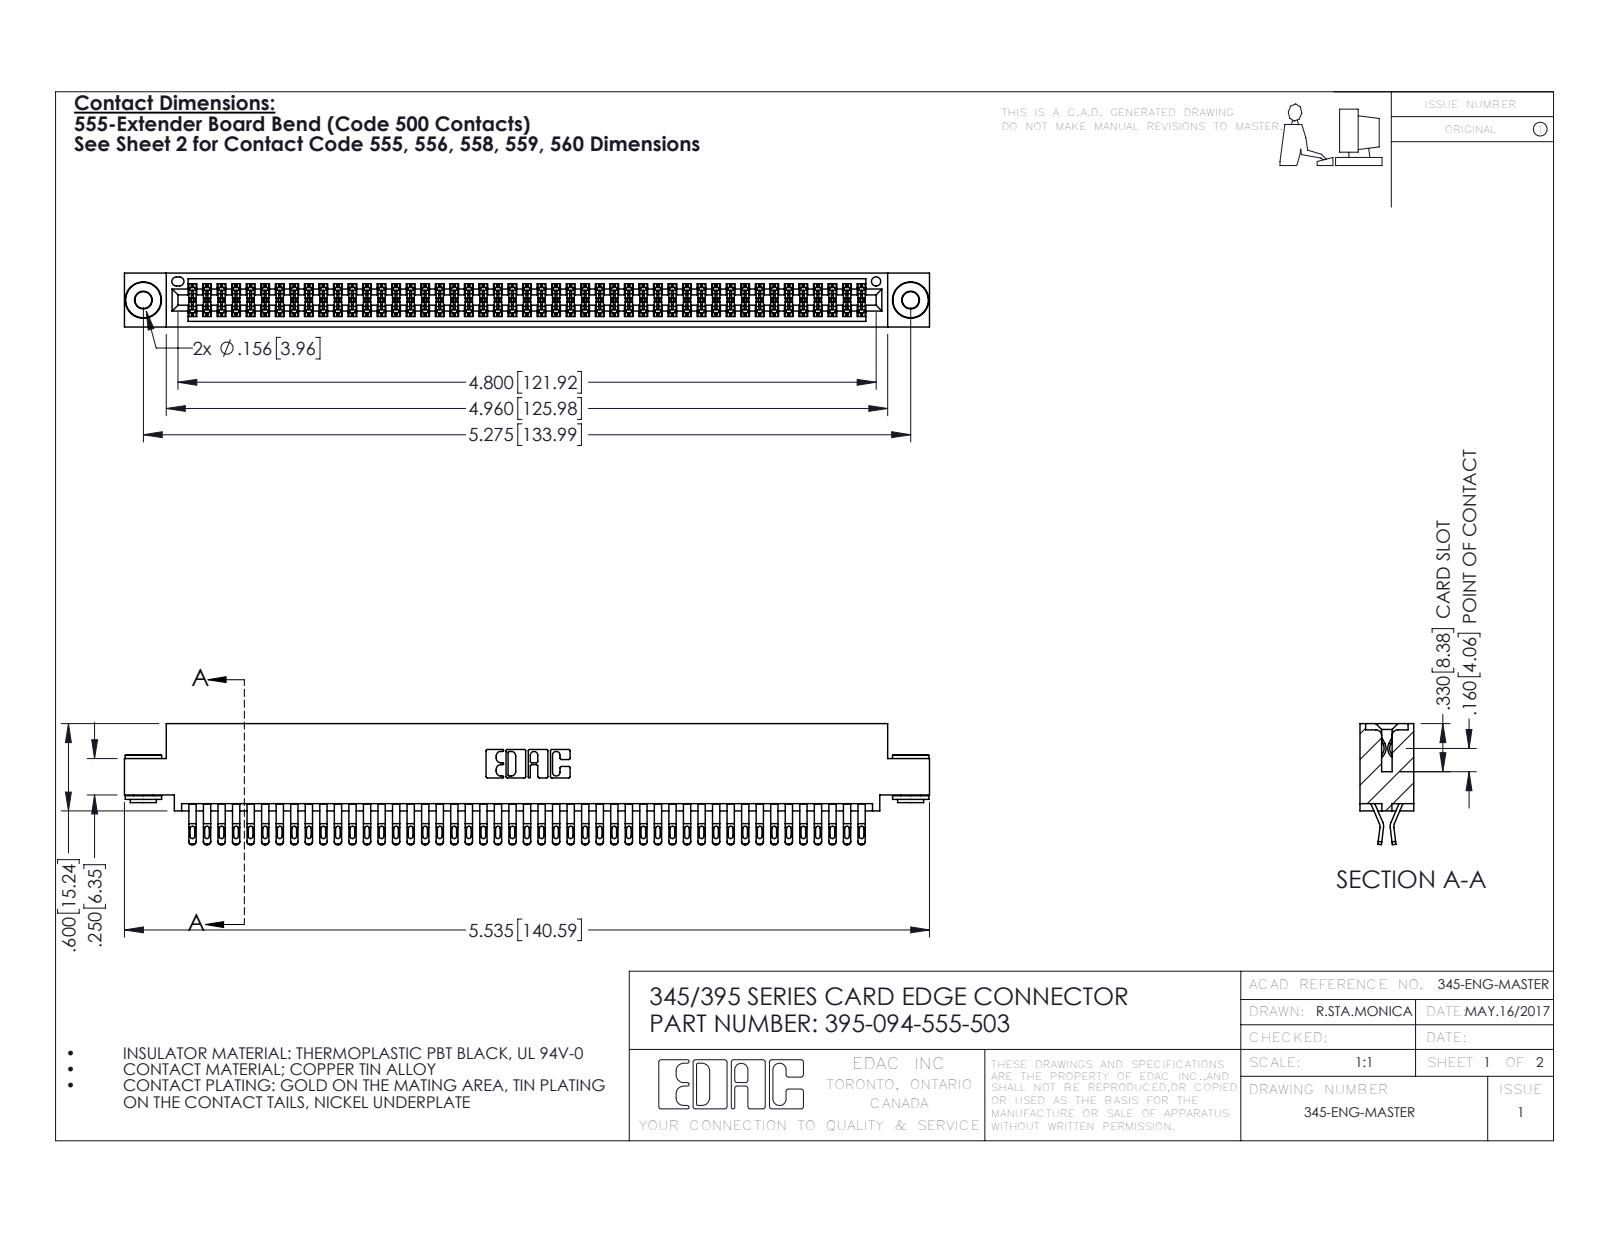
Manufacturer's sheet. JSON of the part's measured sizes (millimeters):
{"part_name": "345 Part_0.110 Offset - 0.156 Dia-TH; 345-292-001_555 Tail; 395-094-555-503; 345-250-002_345-250-002-102", "step_written_by": "SolidWorks 2016 (CONFIG_CONTROL_DESIGN)", "units": "millimeters", "bodies": {"solids": 97, "faces": 5432, "planar": 3008, "cylindrical": 2416, "other": 8}, "overall_size": [140.6, 21.1, 9.4], "volume_mm3": 13900, "surface_area_mm2": 21920, "round_holes": [[2.9, 2], [4, 2], [1.6, 1]], "round_bosses_or_shafts": [[6.4, 2], [4.6, 2], [3.5, 2]], "partial_cylinders_radius": [[0.4, 235], [0.5, 188], [0.2, 141], [0.3, 22], [0.2, 6], [0.8, 6], [0.7, 3], [0.3, 2]], "face_to_face_distances": [1.8, 7.6, 0.6, 9.4, 5.1, 2.5, 6.9, 5.7, 4.4, 3.8], "hole_center_spacings": [6.9, 128, 134]}
